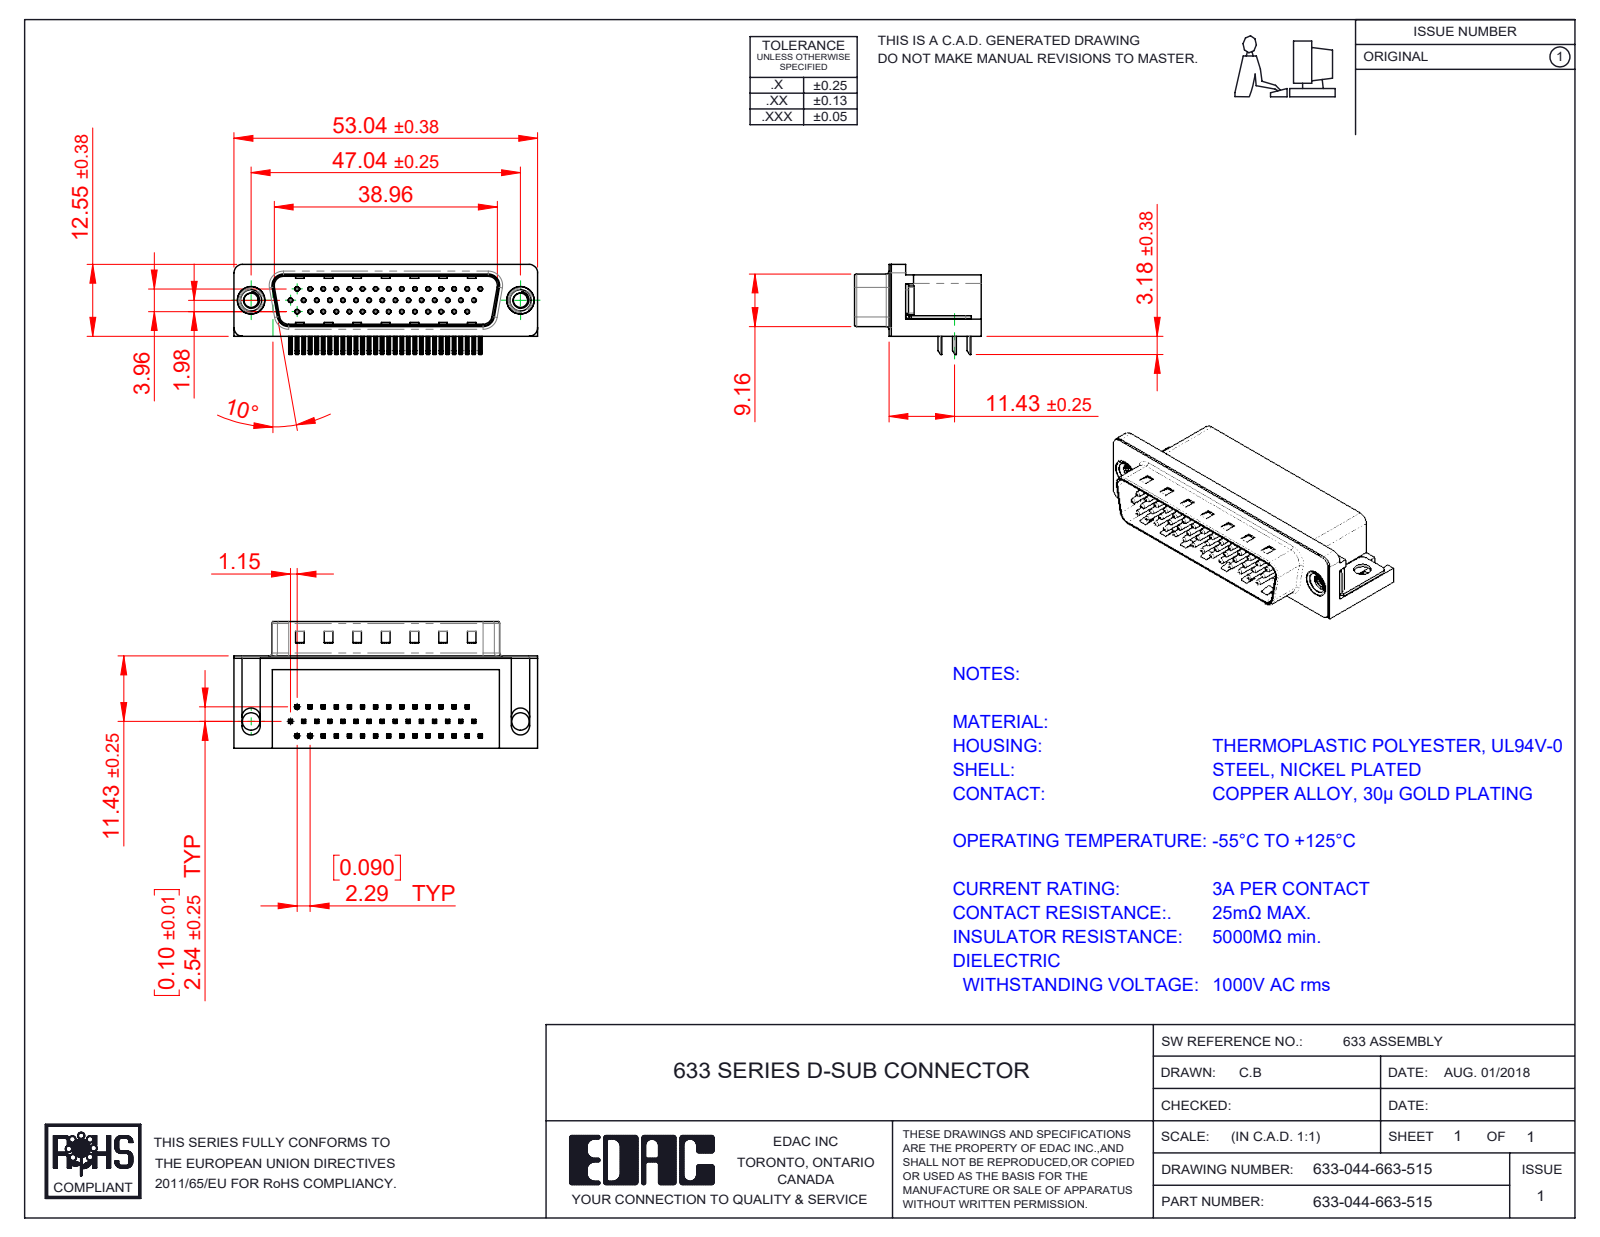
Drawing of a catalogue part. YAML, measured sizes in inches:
part_name: "633 Housing_44 Contact; 633-044-663-515; 633 Shell_44 Contact; 633 Contact Top (+4 more)"
step_written_by: "SolidWorks 2016 (CONFIG_CONTROL_DESIGN)"
units: inches
bodies: {solids: 50, faces: 3688, planar: 2315, cylindrical: 1064, other: 309}
overall_size: [2.088, 0.87, 0.619]
volume: 0.495
surface_area: 15.82
round_holes:
  - {diameter: 0.014, count: 44}
  - {diameter: 0.031, count: 44}
  - {diameter: 0.098, count: 2}
  - {diameter: 0.12, count: 2}
  - {diameter: 0.157, count: 2}
  - {diameter: 0.189, count: 2}
  - {diameter: 0.197, count: 2}
round_bosses_or_shafts:
  - {diameter: 0.03, count: 44}
  - {diameter: 0.193, count: 2}
  - {diameter: 0.187, count: 2}
  - {diameter: 0.154, count: 2}
partial_cylinders:
  - {radius: 0.01, count: 184}
  - {radius: 0.005, count: 88}
  - {radius: 0.039, count: 16}
  - {radius: 0.02, count: 9}
  - {radius: 0.063, count: 8}
  - {radius: 0.059, count: 7}
  - {radius: 0.035, count: 4}
  - {radius: 0.079, count: 4}
face_to_face_distances: [0.016, 0.407, 0.618, 0.114, 0.345, 0.098, 0.083, 0.634, 0.421, 0.1]
hole_center_spacings: [0.09, 0.18, 0.18, 0.09, 0.27, 0.361, 0.451, 0.089]
